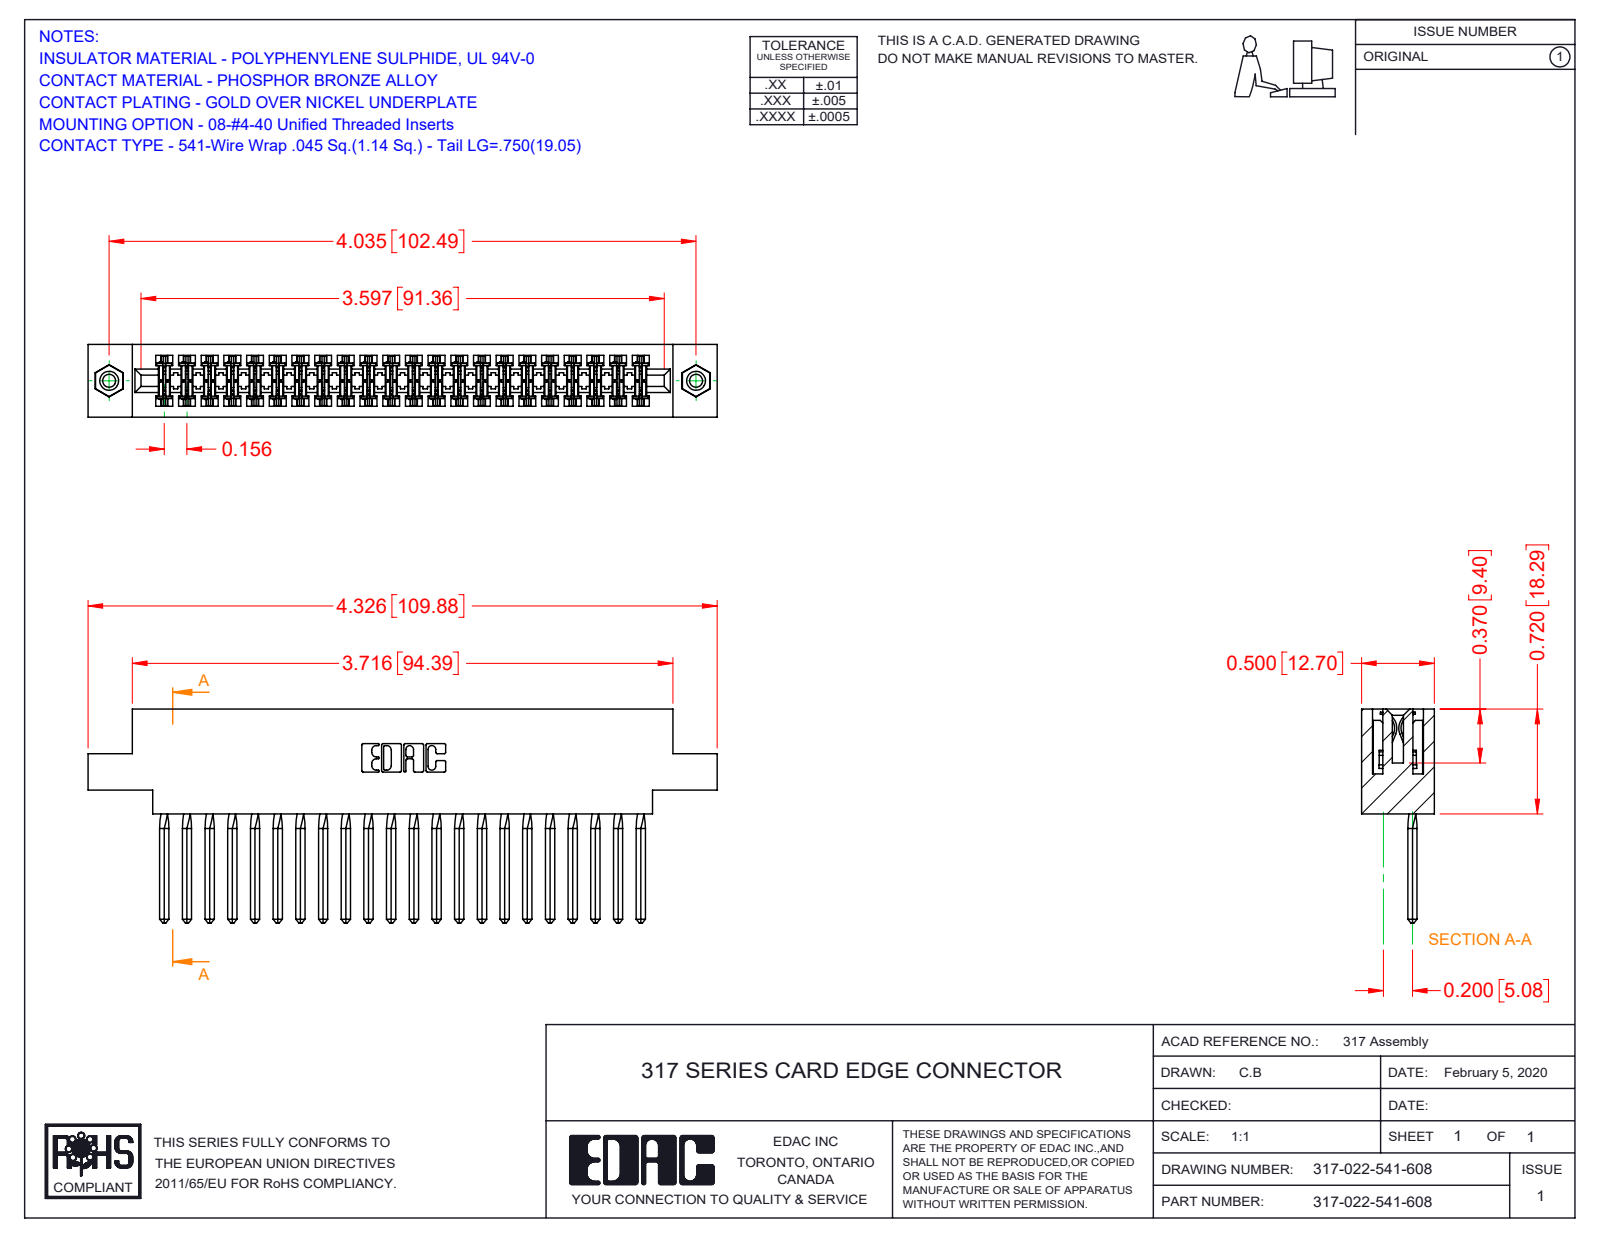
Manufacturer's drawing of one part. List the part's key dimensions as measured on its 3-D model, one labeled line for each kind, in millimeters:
Part name (STEP PRODUCT): 317-290-002_541; 345-250-001_345-250-003-102; 317 Part_.156 Dia - TI; 317-022-541-678
STEP written by: SolidWorks 2016 (CONFIG_CONTROL_DESIGN)
Units: millimetres
Bodies: 25 solids, 3506 faces (2818 planar, 584 cylindrical, 104 other)
Overall size (bounding box): 109.9 × 37.3 × 12.7
Volume: 17 190 mm³ · Surface area: 23 660 mm²
Round holes (diameter × count): ⌀2.3 ×2, ⌀3.2 ×2, ⌀4 ×2
Round bosses / shafts (diameter × count): ⌀3.9 ×2
Partial cylindrical surfaces — rounded edges, fillets, slot ends (radius × count): R0.4 ×44, R0.3 ×22, R0.2 ×6, R0.8 ×6, R0.7 ×3, R2.4 ×2, R2.5 ×2, R2.8 ×2
Main face-to-face distances: 12.7, 1.9, 10.8, 2.8, 8.9, 5, 19.6, 5.6, 16.8, 18.3
Hole centre spacings: 102.5
